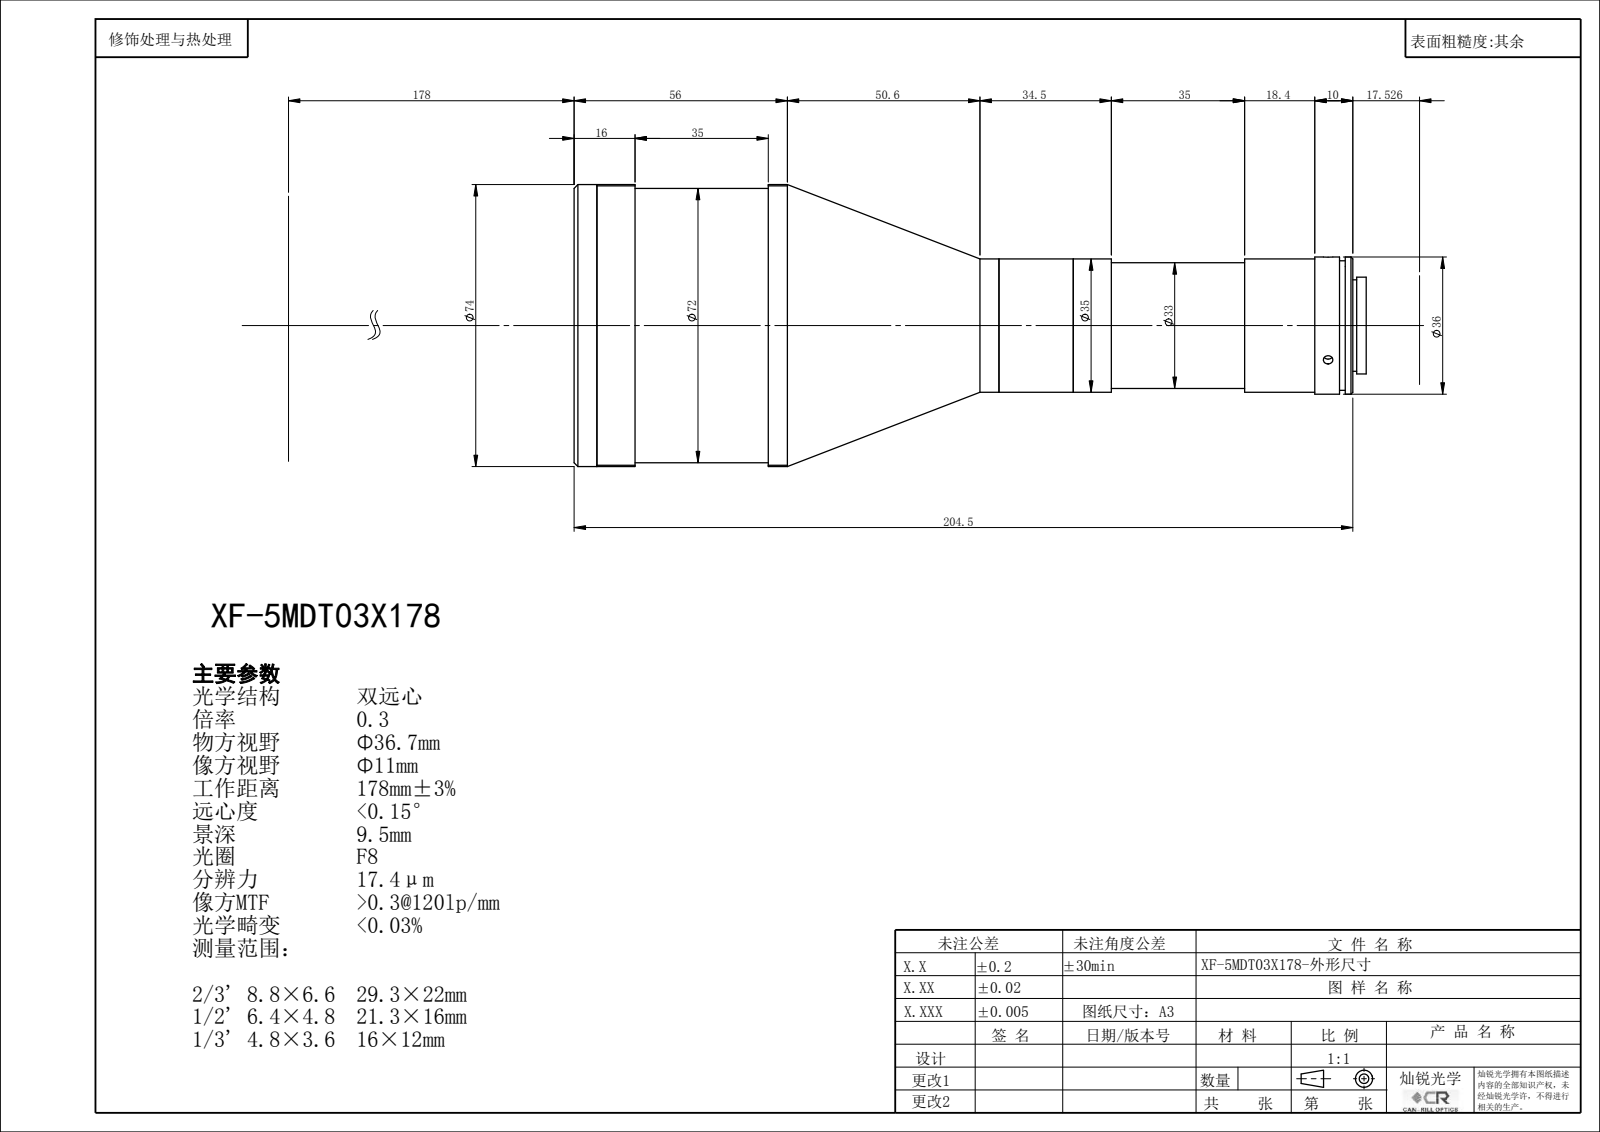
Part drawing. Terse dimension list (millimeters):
name: XF-5MDT03X178
written by: SolidWorks 2014 (CONFIG_CONTROL_DESIGN)
unit: mm
bodies: 0 solids, 86 faces (22 planar, 54 cylindrical, 10 other)
size: 208 × 74 × 74
holes: 3× ⌀2.5, 1× ⌀21.4, 1× ⌀24, 1× ⌀64, 1× ⌀67, 1× ⌀70
bosses: 1× ⌀74, 1× ⌀72, 1× ⌀36, 1× ⌀35, 1× ⌀34, 1× ⌀33, 1× ⌀28, 1× ⌀25.4
face distances: 10, 204.5, 188.5, 125.08, 199.87, 4.63, 63.42, 45, 35, 198.5
